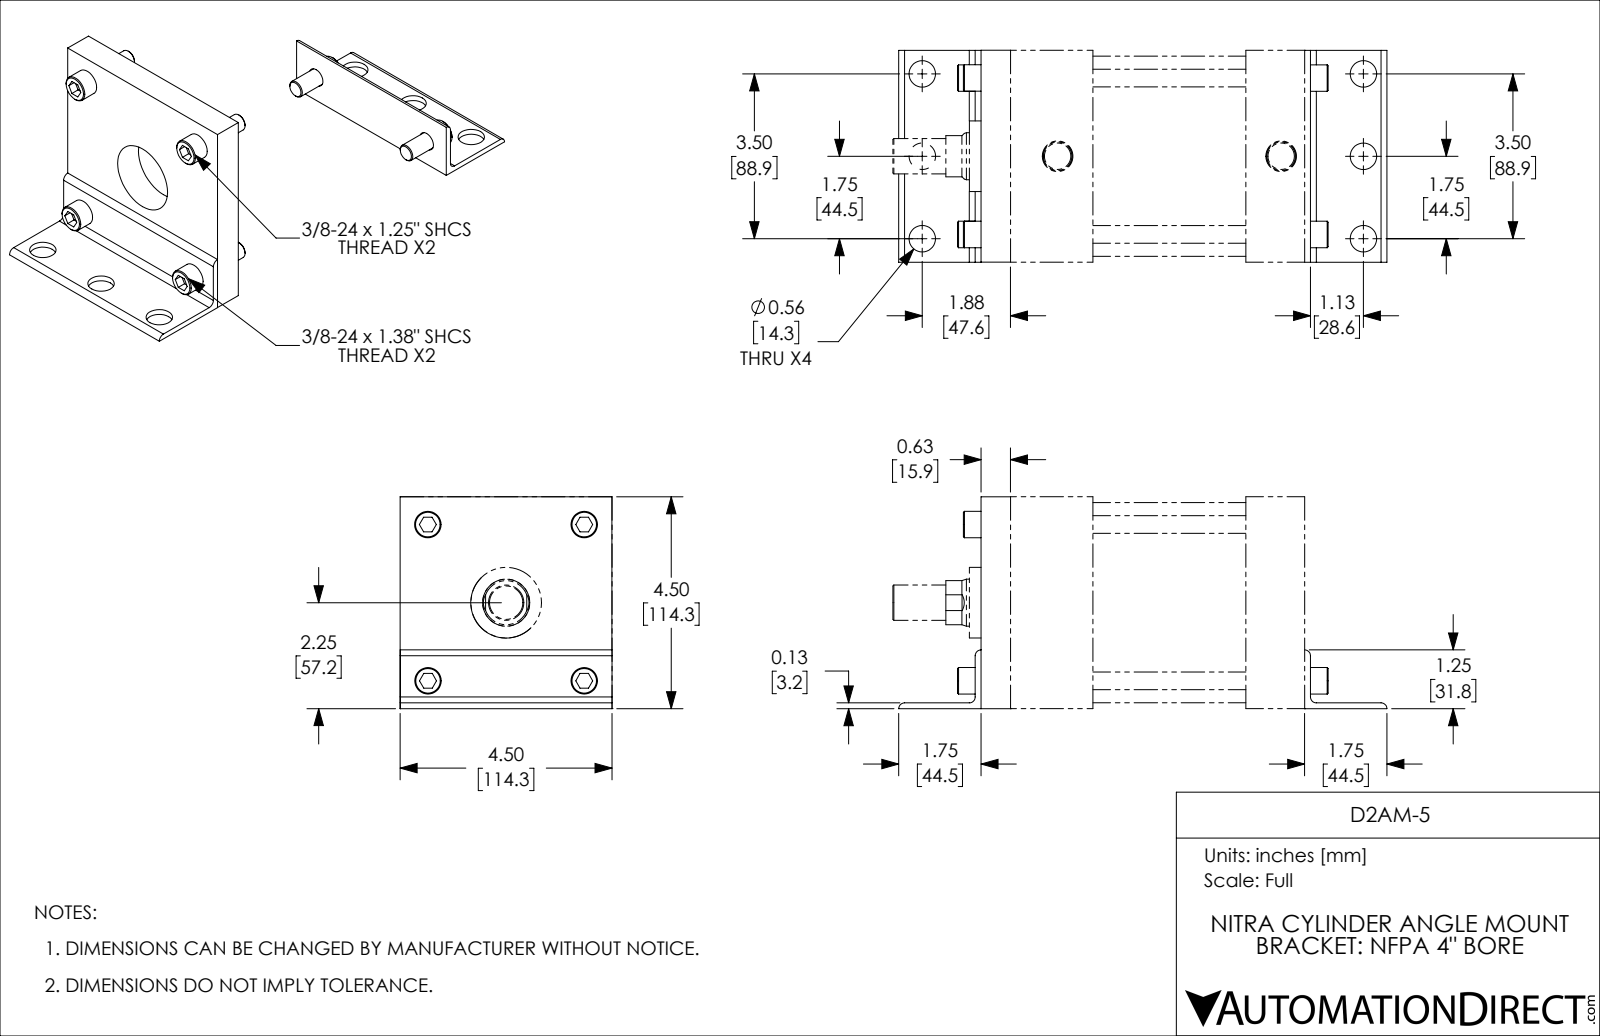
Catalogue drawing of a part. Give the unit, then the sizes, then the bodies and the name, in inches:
Units: inches
Overall size (bounding box): 10.375 × 4.502 × 4.5
Round holes (diameter × count): ⌀0.406 ×6, ⌀0.563 ×6, ⌀1.5 ×1
Round bosses / shafts (diameter × count): ⌀0.562 ×4, ⌀0.375 ×4
Partial cylindrical surfaces — rounded edges, fillets, slot ends (radius × count): R0.125 ×6
Main face-to-face distances: 0.625, 0.125, 7, 4.5, 0.125, 6.25, 6.875, 0.75, 6.375, 7.125
Hole centre spacings: 3.324, 1.75, 2.35, 9.537, 9.375, 3.318, 3.32, 3.5
Volume: 15.39 in³ · Surface area: 121.1 in²
Bodies: 9 solids, 162 faces (78 planar, 60 cylindrical, 24 other)
Part name (STEP PRODUCT): D2AM-5; D2AM-5_2; D2AM-5_1
STEP written by: SolidWorks 2019 (CONFIG_CONTROL_DESIGN)
